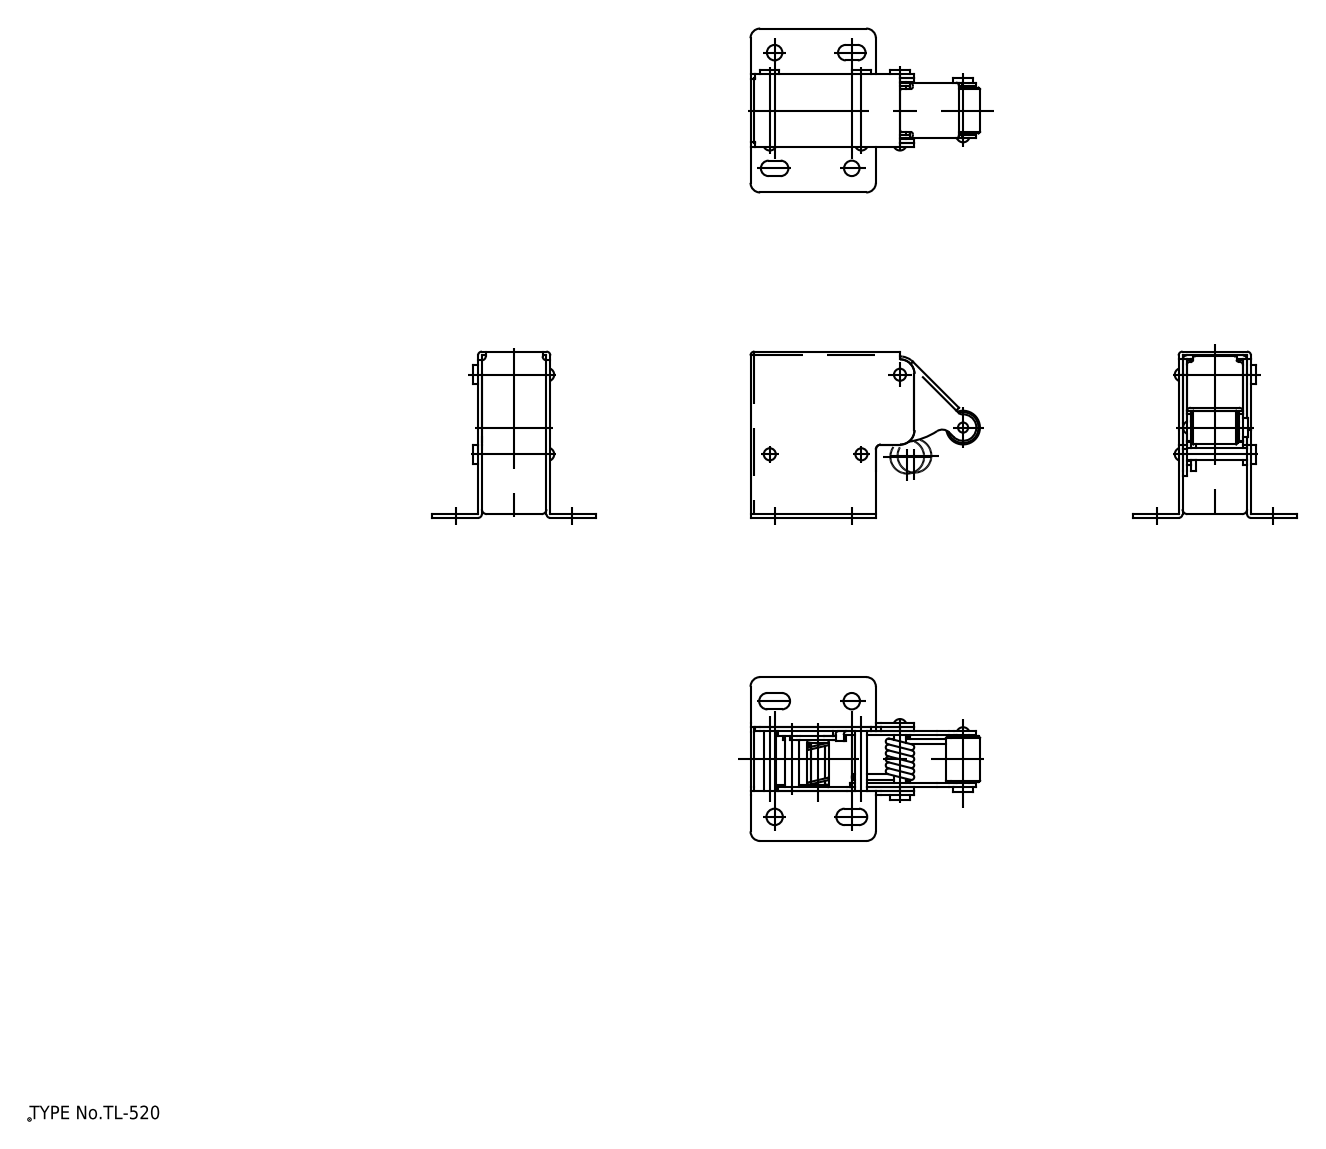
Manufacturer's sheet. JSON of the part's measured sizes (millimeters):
{"part_name": "ボックス; ラッチアーム; ローラー; キーパー (+1 more)", "step_written_by": "spGate 18.9.1 (****-****-****-****) (AUTOMOTIVE_DESIGN)", "units": "millimeters", "bodies": {"solids": 5, "faces": 284, "planar": 106, "cylindrical": 149, "other": 29}, "overall_size": [65.58, 36, 34], "volume_mm3": 6045, "surface_area_mm2": 13255, "round_holes": [[2.1, 4], [2.6, 4], [3.1, 2], [3.2, 2], [2.2, 1], [3.4, 1], [6.5, 1]], "round_bosses_or_shafts": [[4, 4], [2.5, 4], [2, 3], [7, 1]], "partial_cylinders_radius": [[0.5, 20], [1, 13], [0.8, 10], [2, 5], [1.6, 4], [3, 4], [1.7, 2], [3.25, 2]], "face_to_face_distances": [0.8, 0.85, 13.35, 14.2, 12.5, 1.65, 12.55, 14.15, 1.7, 11.65], "hole_center_spacings": [4.67, 5.45, 9.12, 10.11, 14.42, 17.06, 18.34, 19]}
